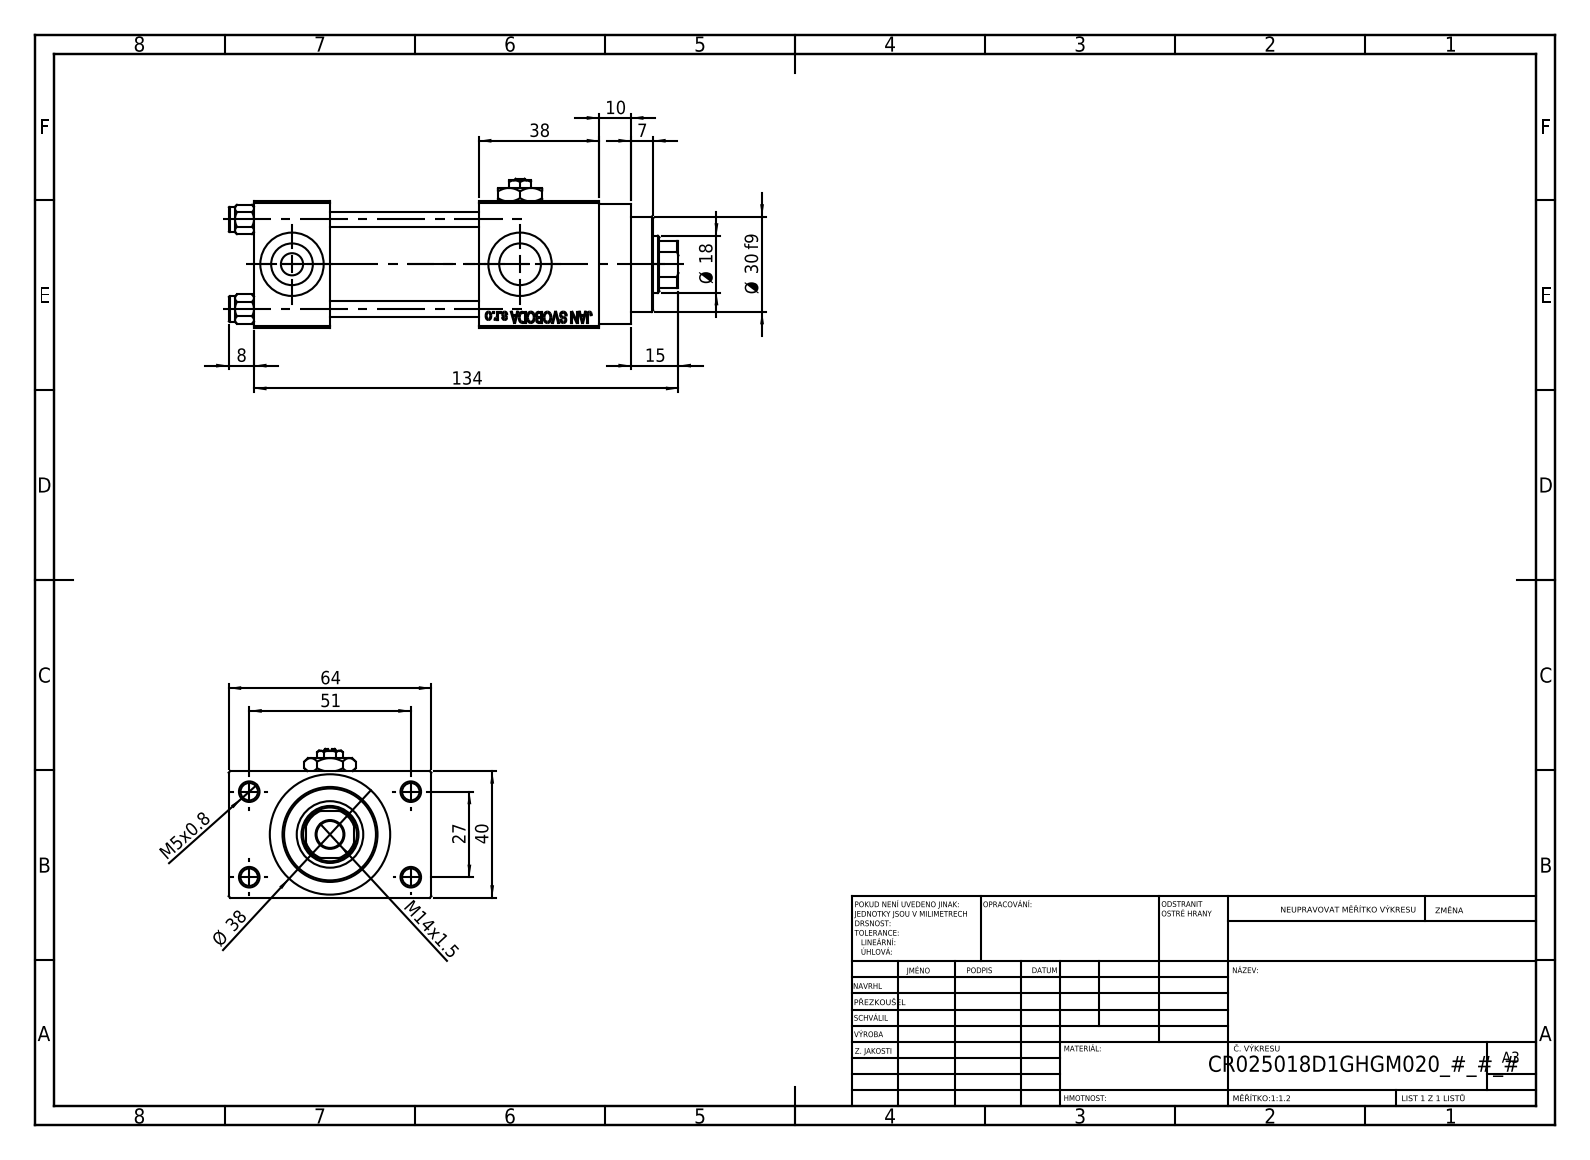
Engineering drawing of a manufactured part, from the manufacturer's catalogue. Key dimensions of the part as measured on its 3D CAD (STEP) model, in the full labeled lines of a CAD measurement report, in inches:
Part name (STEP PRODUCT): V215CR_VCP_D; NUT_M5_D; V215_VC_A; V215CR_D_Body (+2 more)
STEP written by: SolidWorks 2019 (CONFIG_CONTROL_DESIGN)
Units: inches
Bodies: 12 solids, 1146 faces (518 planar, 90 cylindrical, 538 other)
Overall size (bounding box): 5.591 × 2.52 × 1.85
Volume: 10.94 in³ · Surface area: 101.2 in²
Round holes (diameter × count): ⌀0.197 ×4, ⌀0.217 ×4, ⌀0.787 ×4, ⌀0.518 ×3, ⌀0.276 ×2, ⌀0.335 ×1, ⌀0.709 ×1, ⌀0.827 ×1, ⌀0.984 ×1, ⌀1.181 ×1
Round bosses / shafts (diameter × count): ⌀0.315 ×4, ⌀1.496 ×1, ⌀1.22 ×1
Partial cylindrical surfaces — rounded edges, fillets, slot ends (radius × count): R0.335 ×1
Main face-to-face distances: 1.575, 0.472, 1.85, 0.945, 2.795, 2.047, 1.496, 3.346, 4.291, 2.52
Hole centre spacings: 0.448, 0.788, 1.114, 1.136, 1.177, 1.561, 1.903, 1.063
